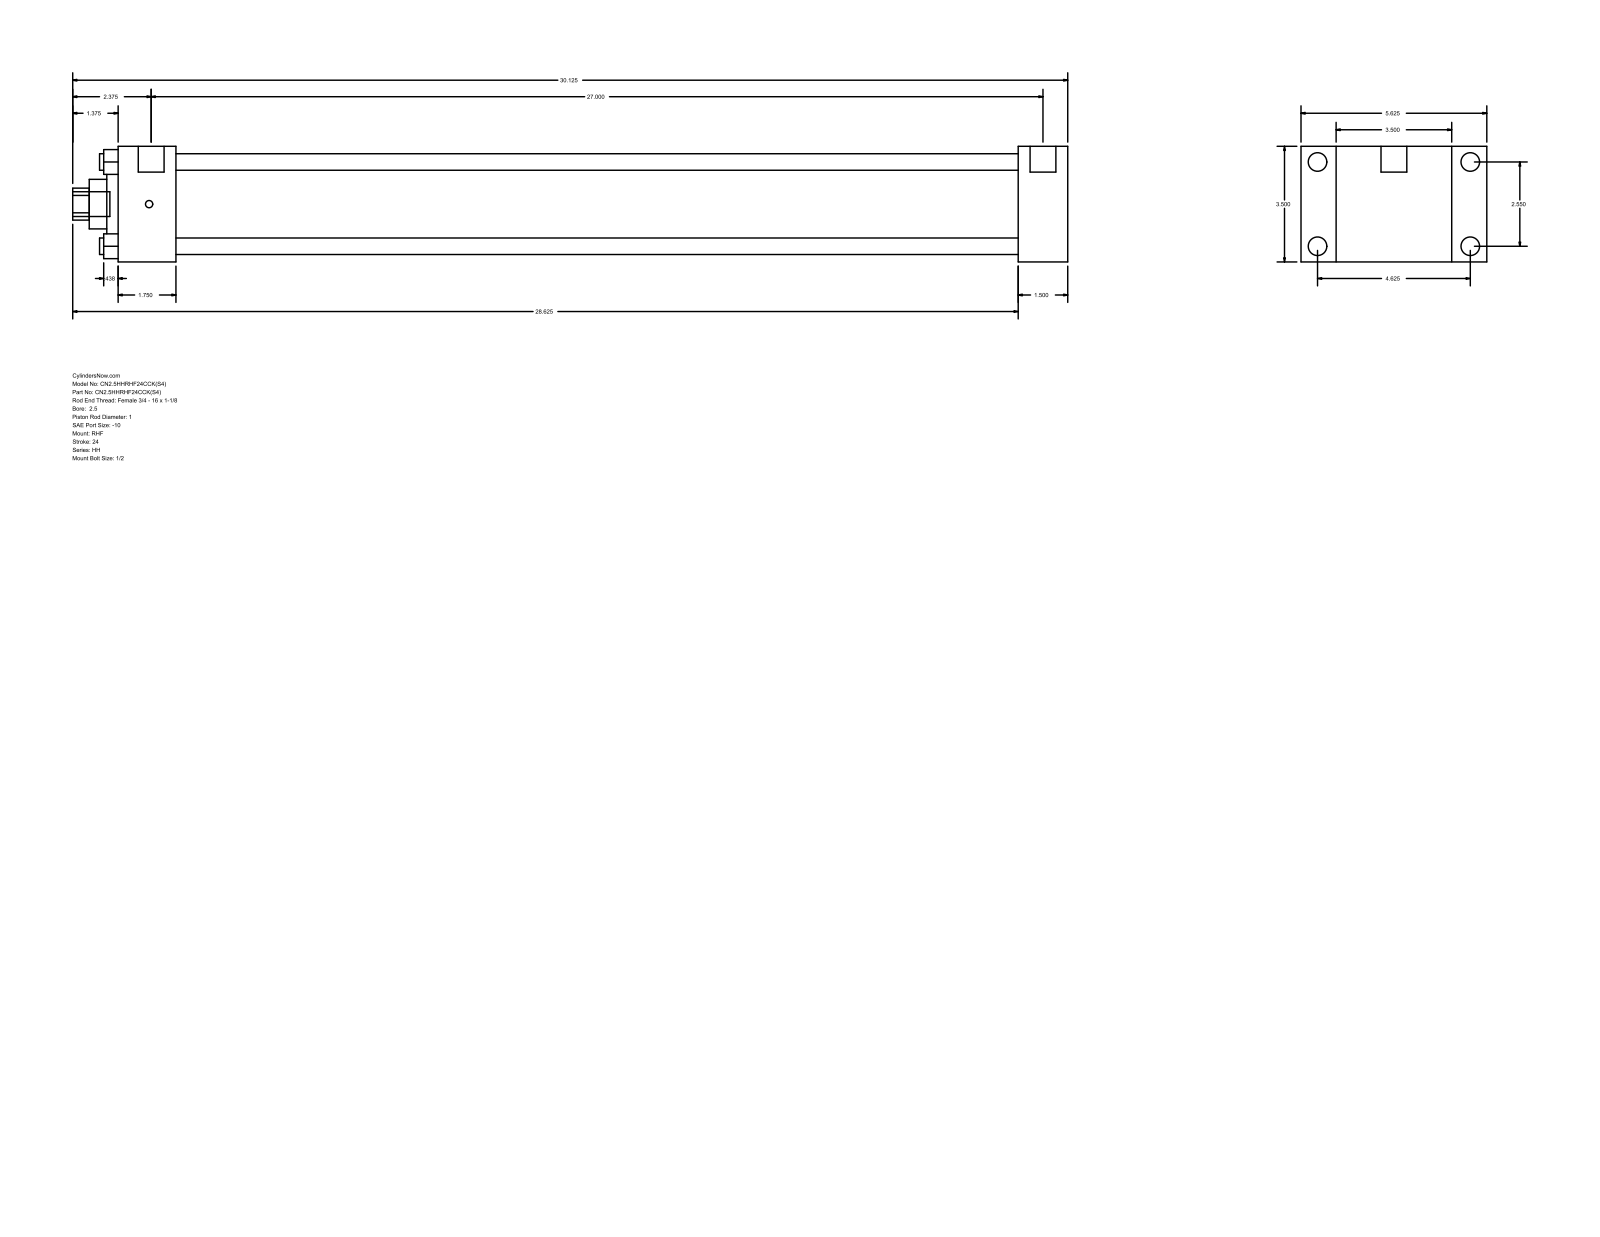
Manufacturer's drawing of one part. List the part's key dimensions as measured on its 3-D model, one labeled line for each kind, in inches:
Part name (STEP PRODUCT): HH_RHF__0250_1
STEP written by: GSSL Pune (CONFIG_CONTROL_DESIGN)
Units: inches
Bodies: 0 solids, 90 faces (61 planar, 29 cylindrical, 0 other)
Overall size (bounding box): 30.125 × 5.625 × 3.5
Round holes (diameter × count): ⌀0.5 ×4, ⌀1 ×1, ⌀1.5 ×1, ⌀2.375 ×1, ⌀2.875 ×1
Round bosses / shafts (diameter × count): ⌀0.563 ×4, ⌀0.219 ×4, ⌀0.781 ×2, ⌀0.75 ×1
Partial cylindrical surfaces — rounded edges, fillets, slot ends (radius × count): R0.484 ×1
Main face-to-face distances: 3.5, 1.5, 1.063, 4.563, 27.25, 28.75, 5.625, 1.75, 25.5, 27
Hole centre spacings: 1.803, 2.55, 3.606
